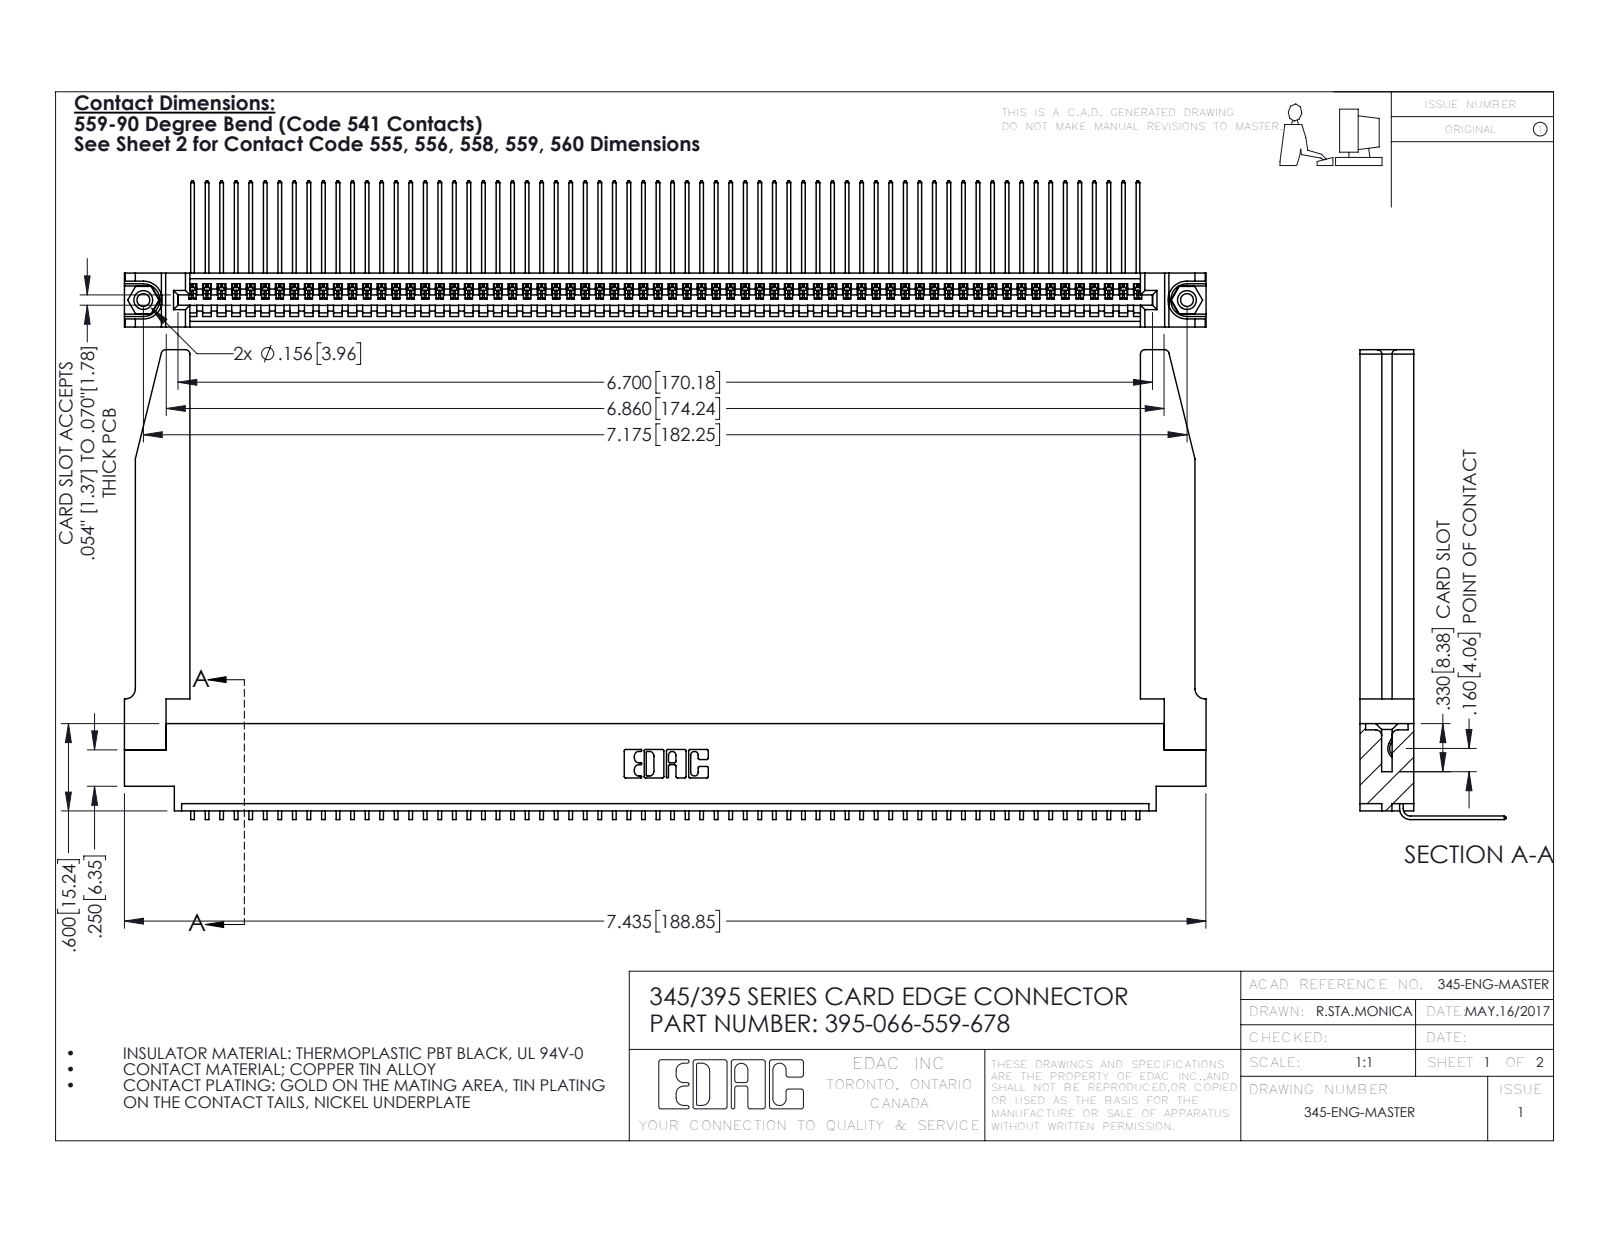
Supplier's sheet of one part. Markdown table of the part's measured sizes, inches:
| quantity | value |
| --- | --- |
| part name | 345-220-078_345-220-078; 345-250-001_345-250-001-102; 345 Part_0.170 Offset - 0.156 Dia-TH; 345-292-001_558 559 Tail - 1 (+1 more) |
| STEP written by | SolidWorks 2016 (CONFIG_CONTROL_DESIGN) |
| units | inches |
| bodies | 71 solids, 4324 faces (2998 planar, 1274 cylindrical, 52 other) |
| overall size | 7.436 × 3.229 × 1.005 |
| volume | 1.587 in³ |
| surface area | 50.89 in² |
| round holes (diameter × count) | 0.089 × 2, 0.125 × 2, 0.156 × 2, 0.064 × 1 |
| round bosses / shafts (diameter × count) | 0.155 × 2 |
| partial cylindrical surfaces (radius × count) | 0.006 × 132, 0.01 × 22, 0.03 × 8, 0.007 × 6, 0.031 × 6, 0.026 × 3, 0.031 × 2, 0.04 × 2 |
| main face-to-face distances | 0.37, 0.072, 0.298, 0.098, 0.272, 0.025, 0.2, 0.225, 0.175, 0.15 |
| hole center spacings | 0.27, 6.939, 7.175 |
